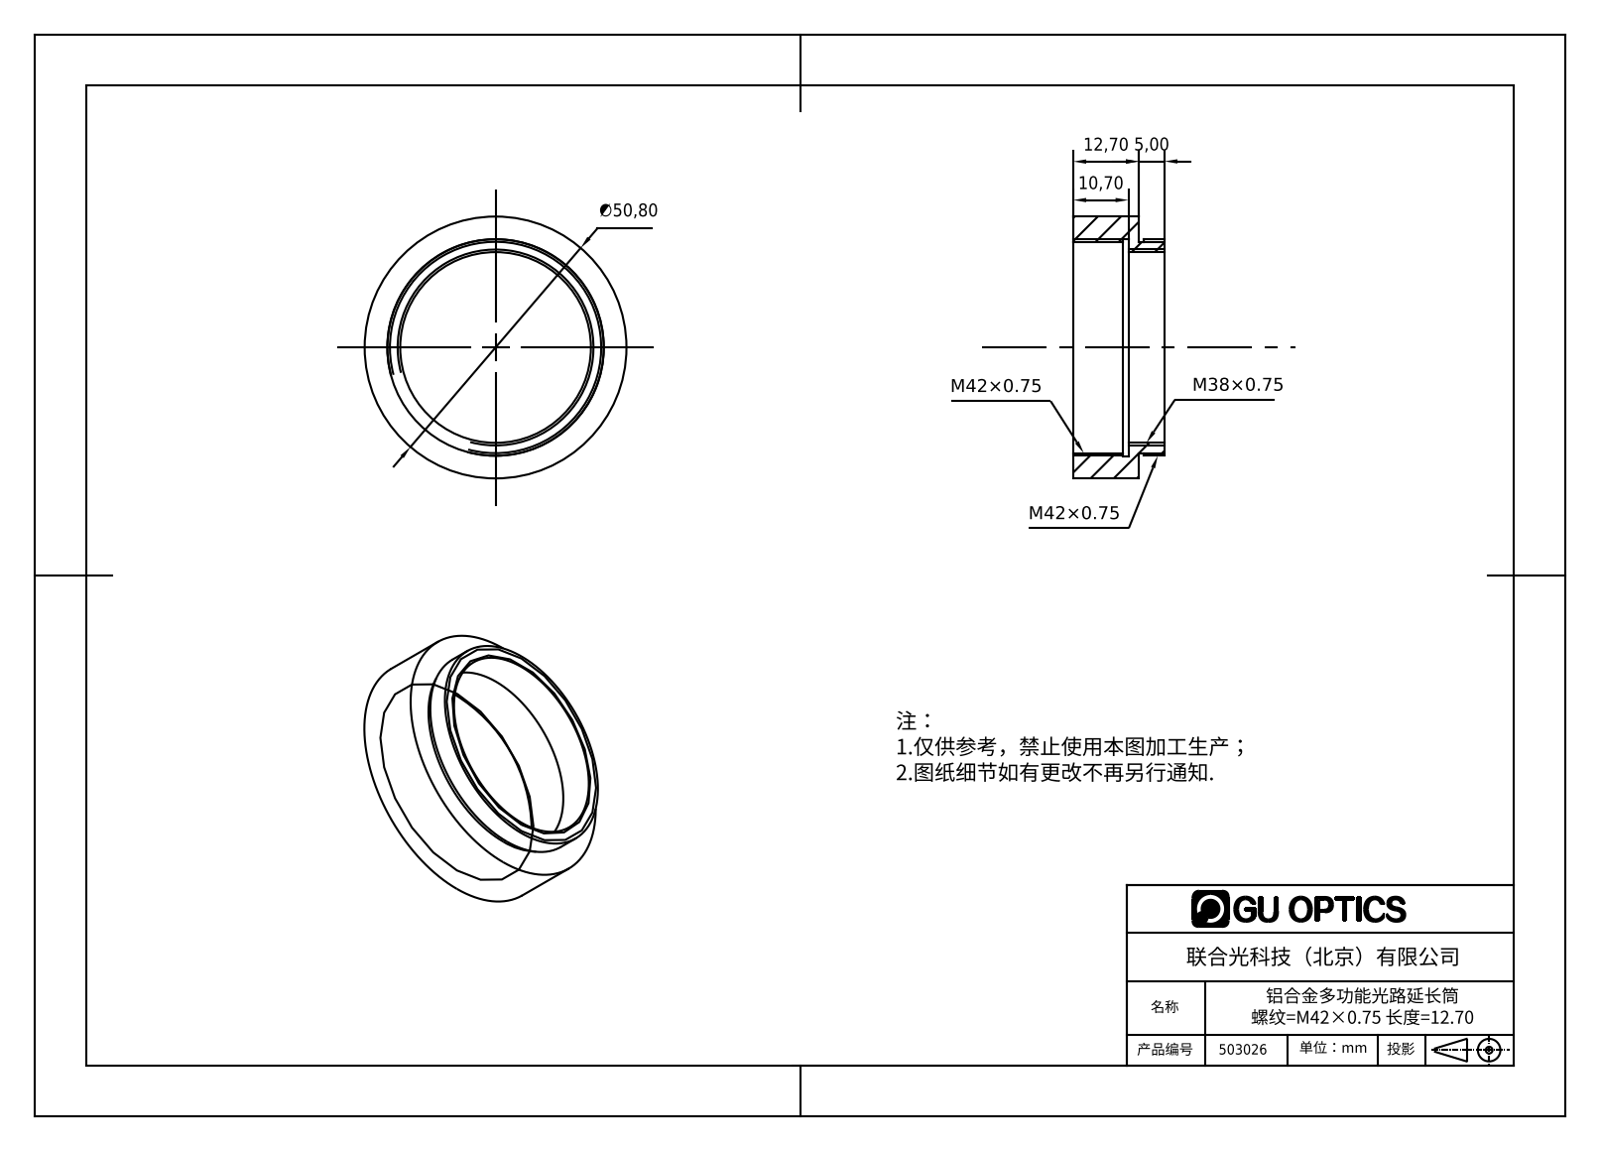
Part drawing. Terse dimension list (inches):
name: 503026
written by: SolidWorks 2016 (AUTOMOTIVE_DESIGN)
unit: in
bodies: 1 solid, 18 faces (6 planar, 12 cylindrical, 0 other)
size: 2 × 2 × 0.697
volume: 0.663 in³; area: 10.96 in²
holes: 1× ⌀1.457, 1× ⌀1.614, 1× ⌀1.661
bosses: 1× ⌀2, 1× ⌀1.654
face distances: 0.5, 0.421, 0.079, 0.697, 0.276, 0.197, 0.039, 0.118, 0.157, 0.382
